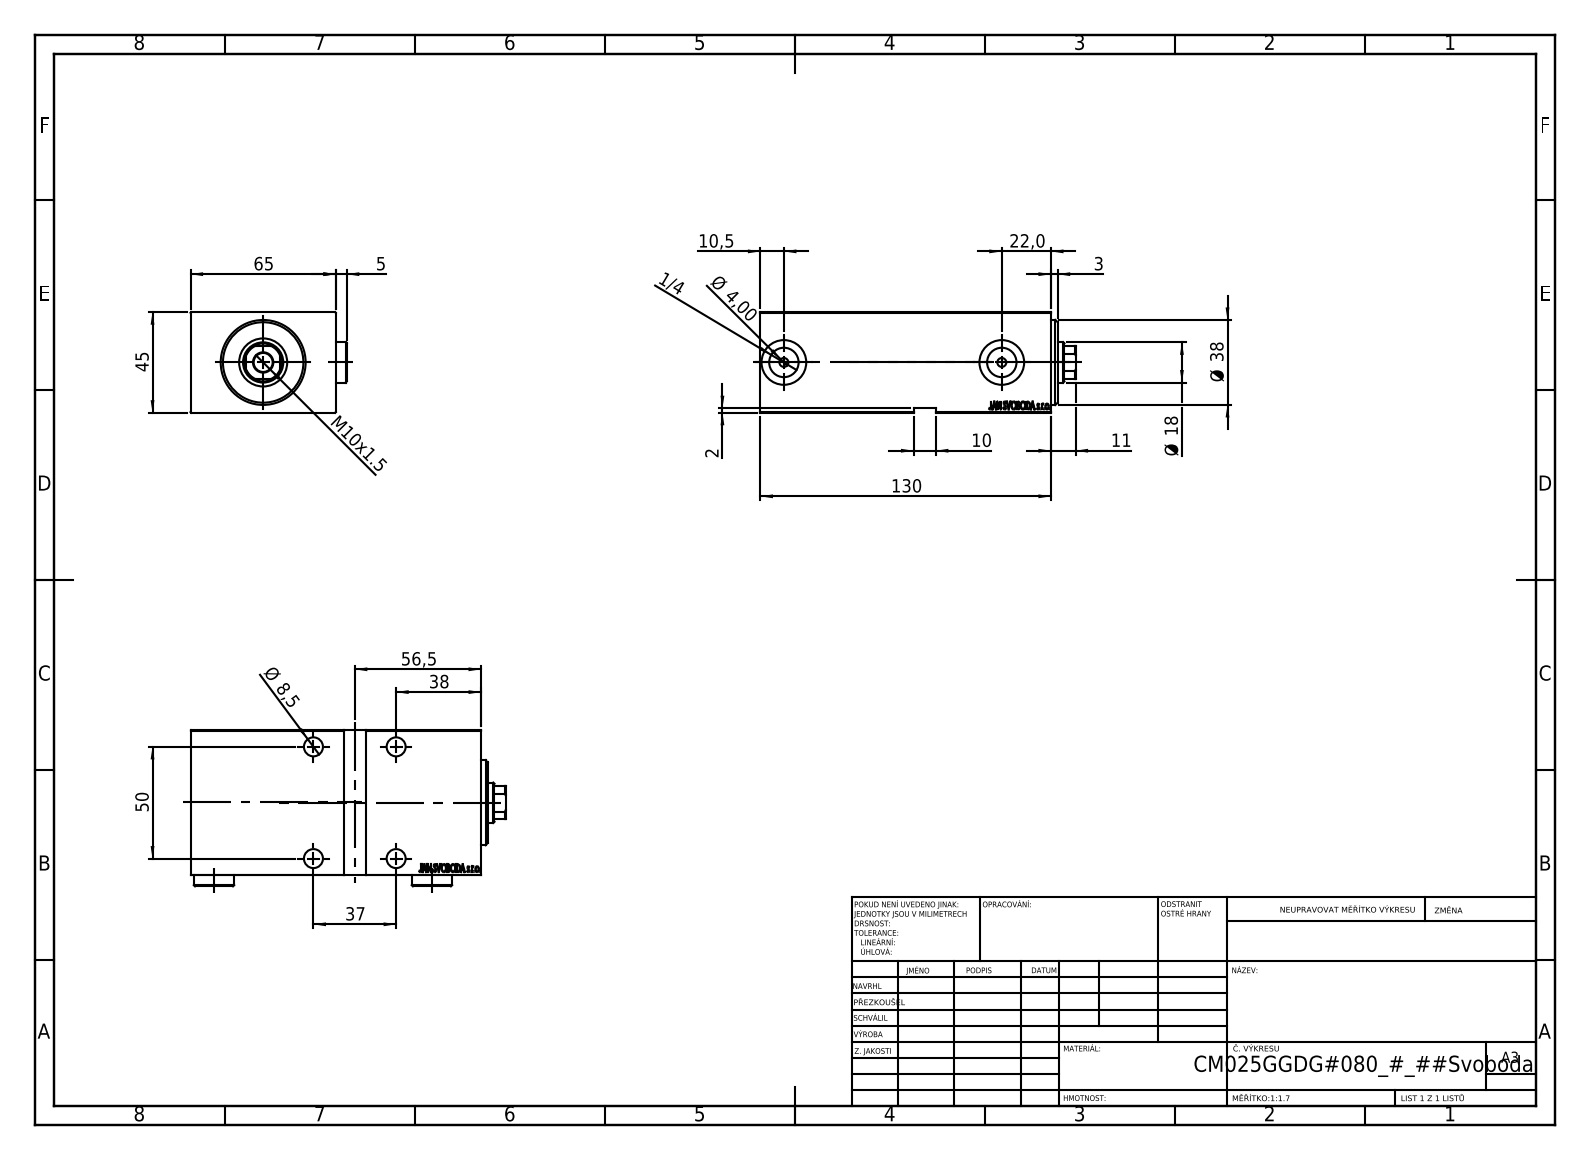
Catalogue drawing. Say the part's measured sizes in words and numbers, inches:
The part is named "V450CM_VC_G; V450CM_G_VCP; Zatka_OIL_PORT; V450CM_G_Body". Its 3-D file was written by "SolidWorks 2019 (CONFIG_CONTROL_DESIGN)". It is 5 solids with 913 faces: 445 planar, 70 cylindrical and 398 other. Overall it measures 5.551 by 2.752 by 1.772 inches. Its volume is 21.02 cubic inches and its surface area 104.5 square inches. Round holes: 5 of diameter 0.335, 4 of diameter 0.531, 2 of diameter 0.157, 2 of diameter 0.518, 2 of diameter 0.787, 1 of diameter 0.709, 1 of diameter 0.846, 1 of diameter 0.984, 1 of diameter 1.063, 1 of diameter 1.378. Round bosses or shafts: 2 of diameter 0.709, 1 of diameter 1.496. Partial cylindrical surfaces (rounded edges, fillets, slot ends): 1 of radius 0.335. The main face-to-face distances are 1.772, 2.559, 5.118, 0.236, 2.555, 4.685, 0.197, 4.882, 0.315, 4.921. The hole center spacings are 1.457, 1.969, 2.449, 3.839.
